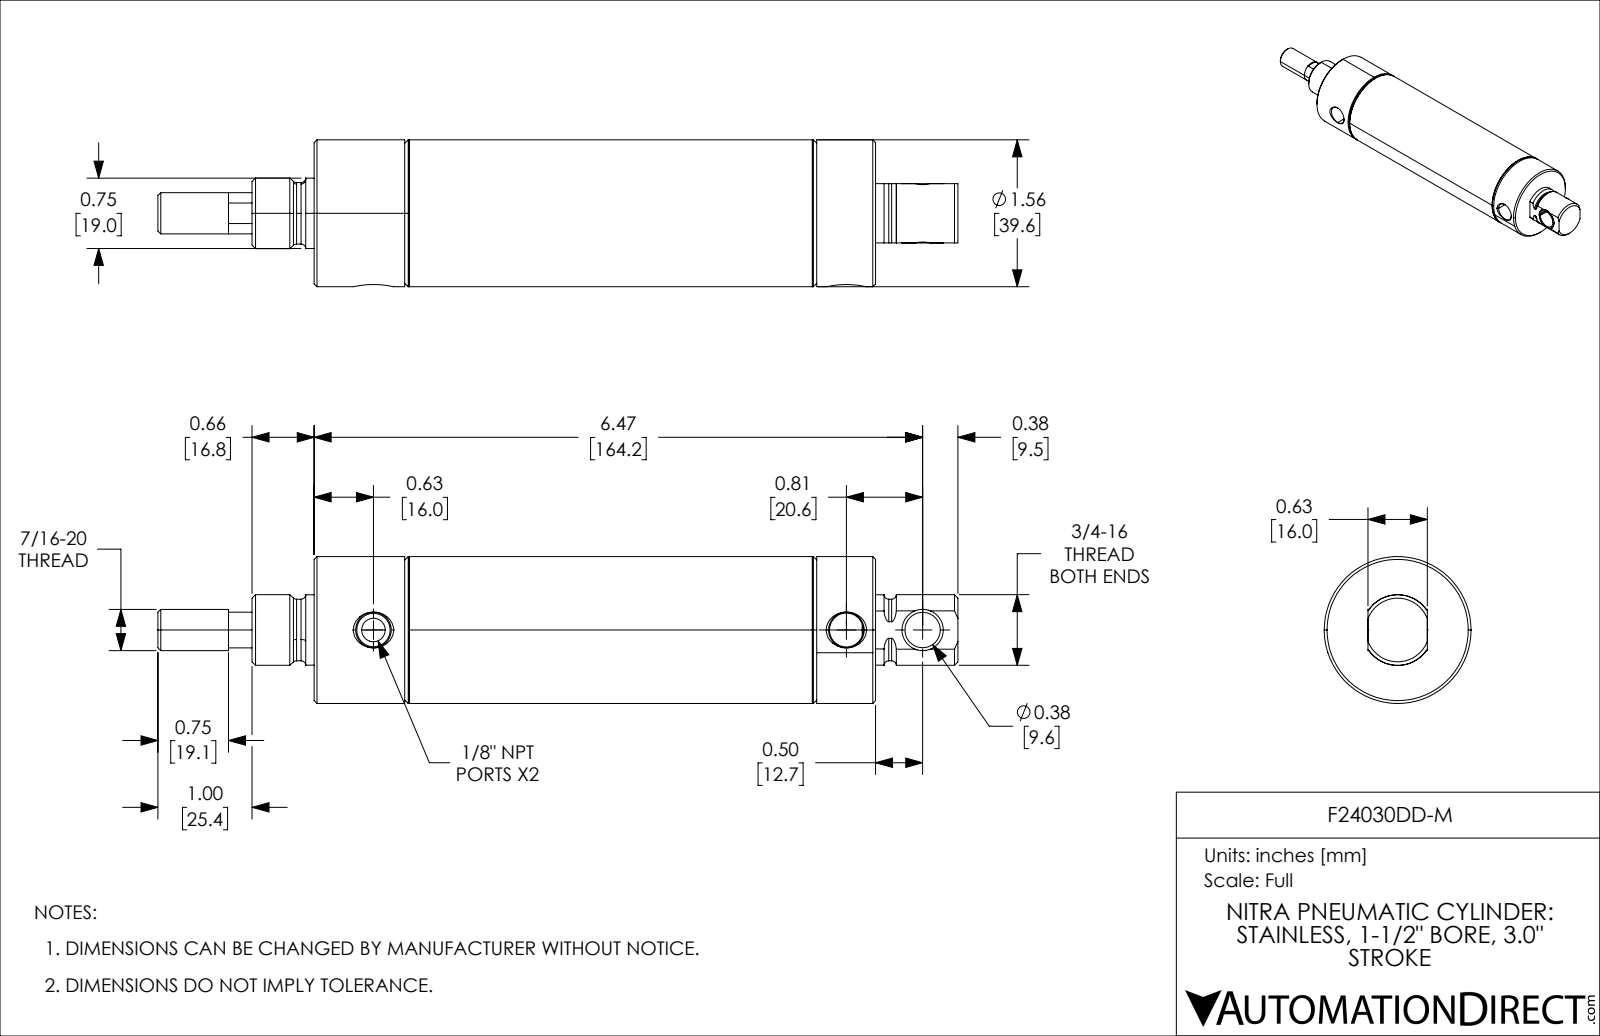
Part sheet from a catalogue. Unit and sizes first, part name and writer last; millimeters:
Units: millimetres
Overall size (bounding box): 215.9 × 39.62 × 39.62
Round holes (diameter × count): ⌀6.35 ×1, ⌀9.14 ×1, ⌀9.55 ×1, ⌀11.15 ×1, ⌀11.73 ×1, ⌀13.51 ×1, ⌀26.97 ×1, ⌀36.36 ×1
Round bosses / shafts (diameter × count): ⌀39.62 ×1, ⌀38.39 ×1, ⌀19.05 ×1, ⌀18.99 ×1, ⌀16.61 ×1, ⌀16.6 ×1, ⌀11.13 ×1, ⌀11.11 ×1
Main face-to-face distances: 22.22, 44.45, 76.2, 98.42, 120.65, 22.23, 30.86, 107.06, 129.28, 151.51
Hole centre spacings: 20.57, 127.64, 148.21
Volume: 108 772 mm³ · Surface area: 56 951 mm²
Bodies: 5 solids, 157 faces (35 planar, 58 cylindrical, 64 other)
Part name (STEP PRODUCT): F24030DD-M_9; F24030DD-M; F24030DD-M_5; F24030DD-M_7 (+2 more)
STEP written by: SolidWorks 2021 (CONFIG_CONTROL_DESIGN)
